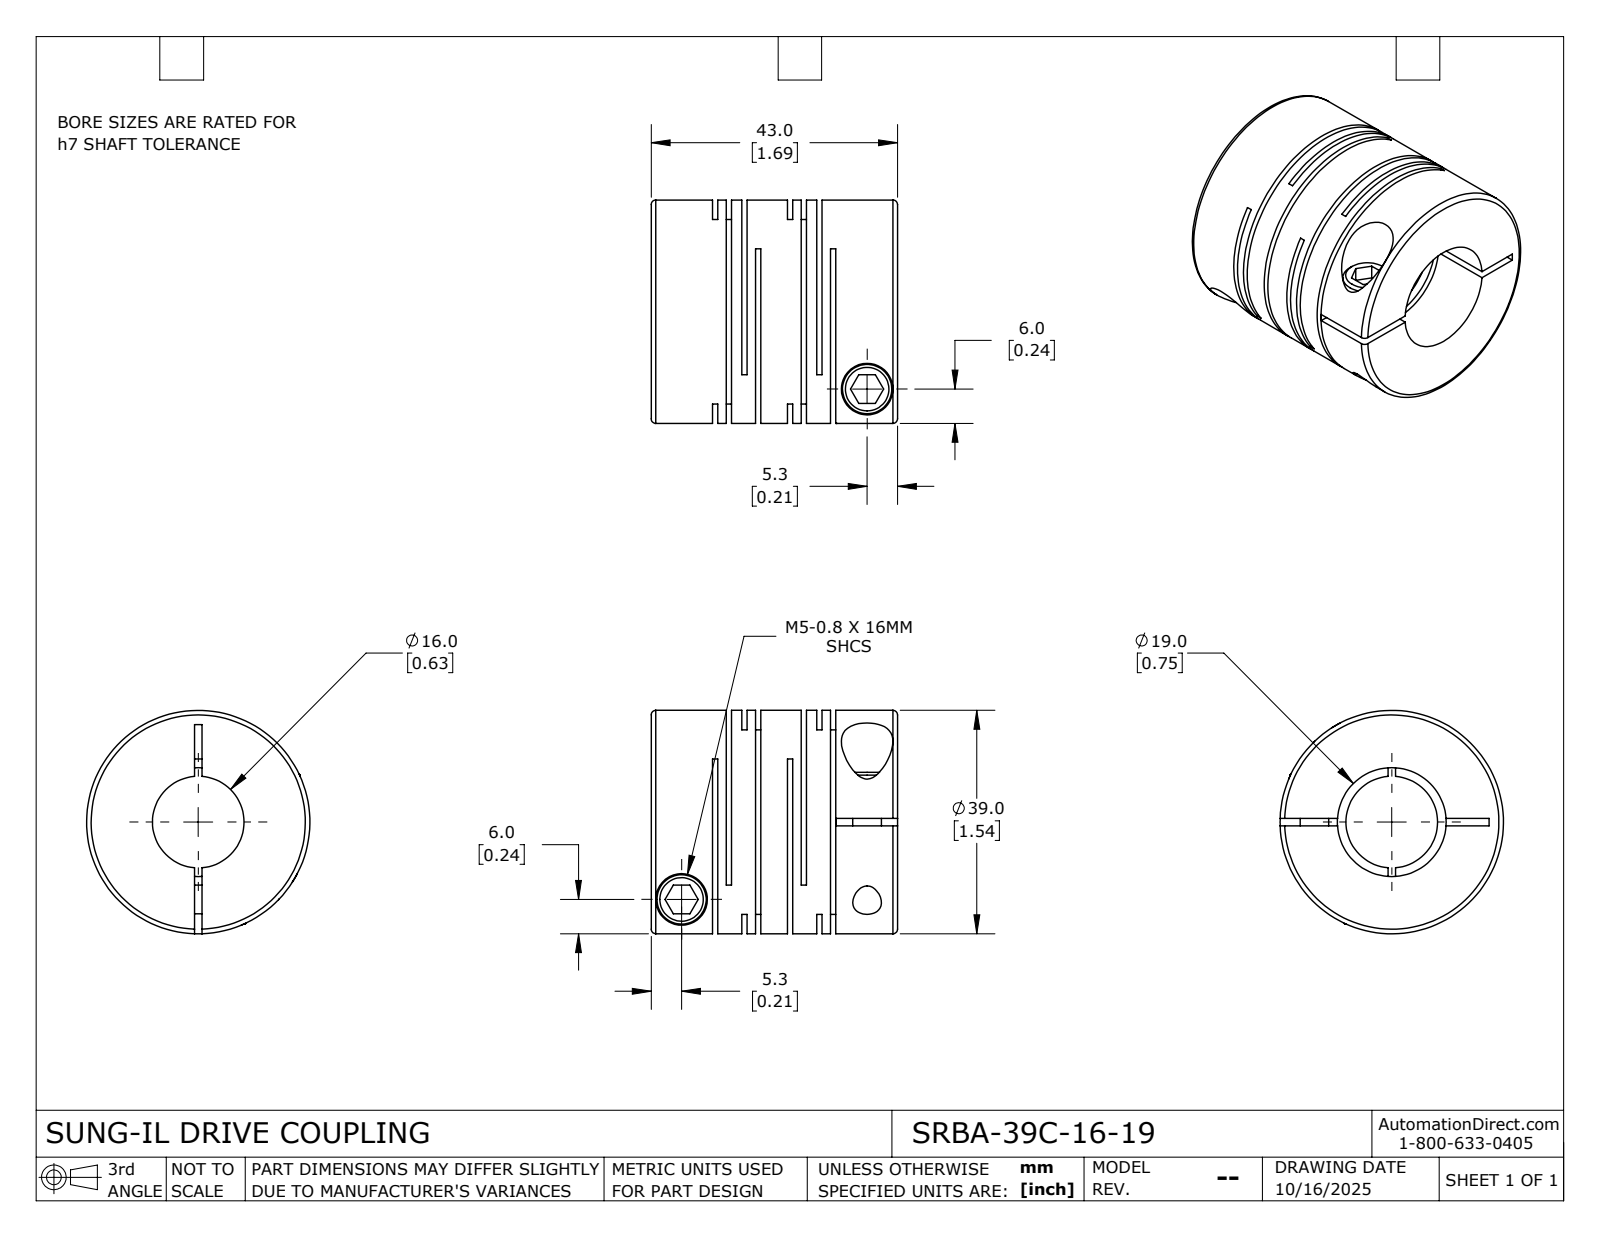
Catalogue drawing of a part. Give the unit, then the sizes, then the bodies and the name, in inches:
Units: inches
Overall size (bounding box): 1.693 × 1.535 × 1.535
Round holes (diameter × count): ⌀0.197 ×2, ⌀0.354 ×2, ⌀0.63 ×1, ⌀0.748 ×1
Round bosses / shafts (diameter × count): ⌀0.339 ×2, ⌀1.535 ×1
Main face-to-face distances: 0.516, 0.036, 0.094, 0.201, 0.421, 0.552, 0.717, 0.48, 0.131, 0.295
Volume: 2.035 in³ · Surface area: 33.79 in²
Bodies: 1 solid, 115 faces (60 planar, 42 cylindrical, 13 other)
Part name (STEP PRODUCT): SRBA-39C-16-19
STEP written by: SolidWorks 2024 (CONFIG_CONTROL_DESIGN)
